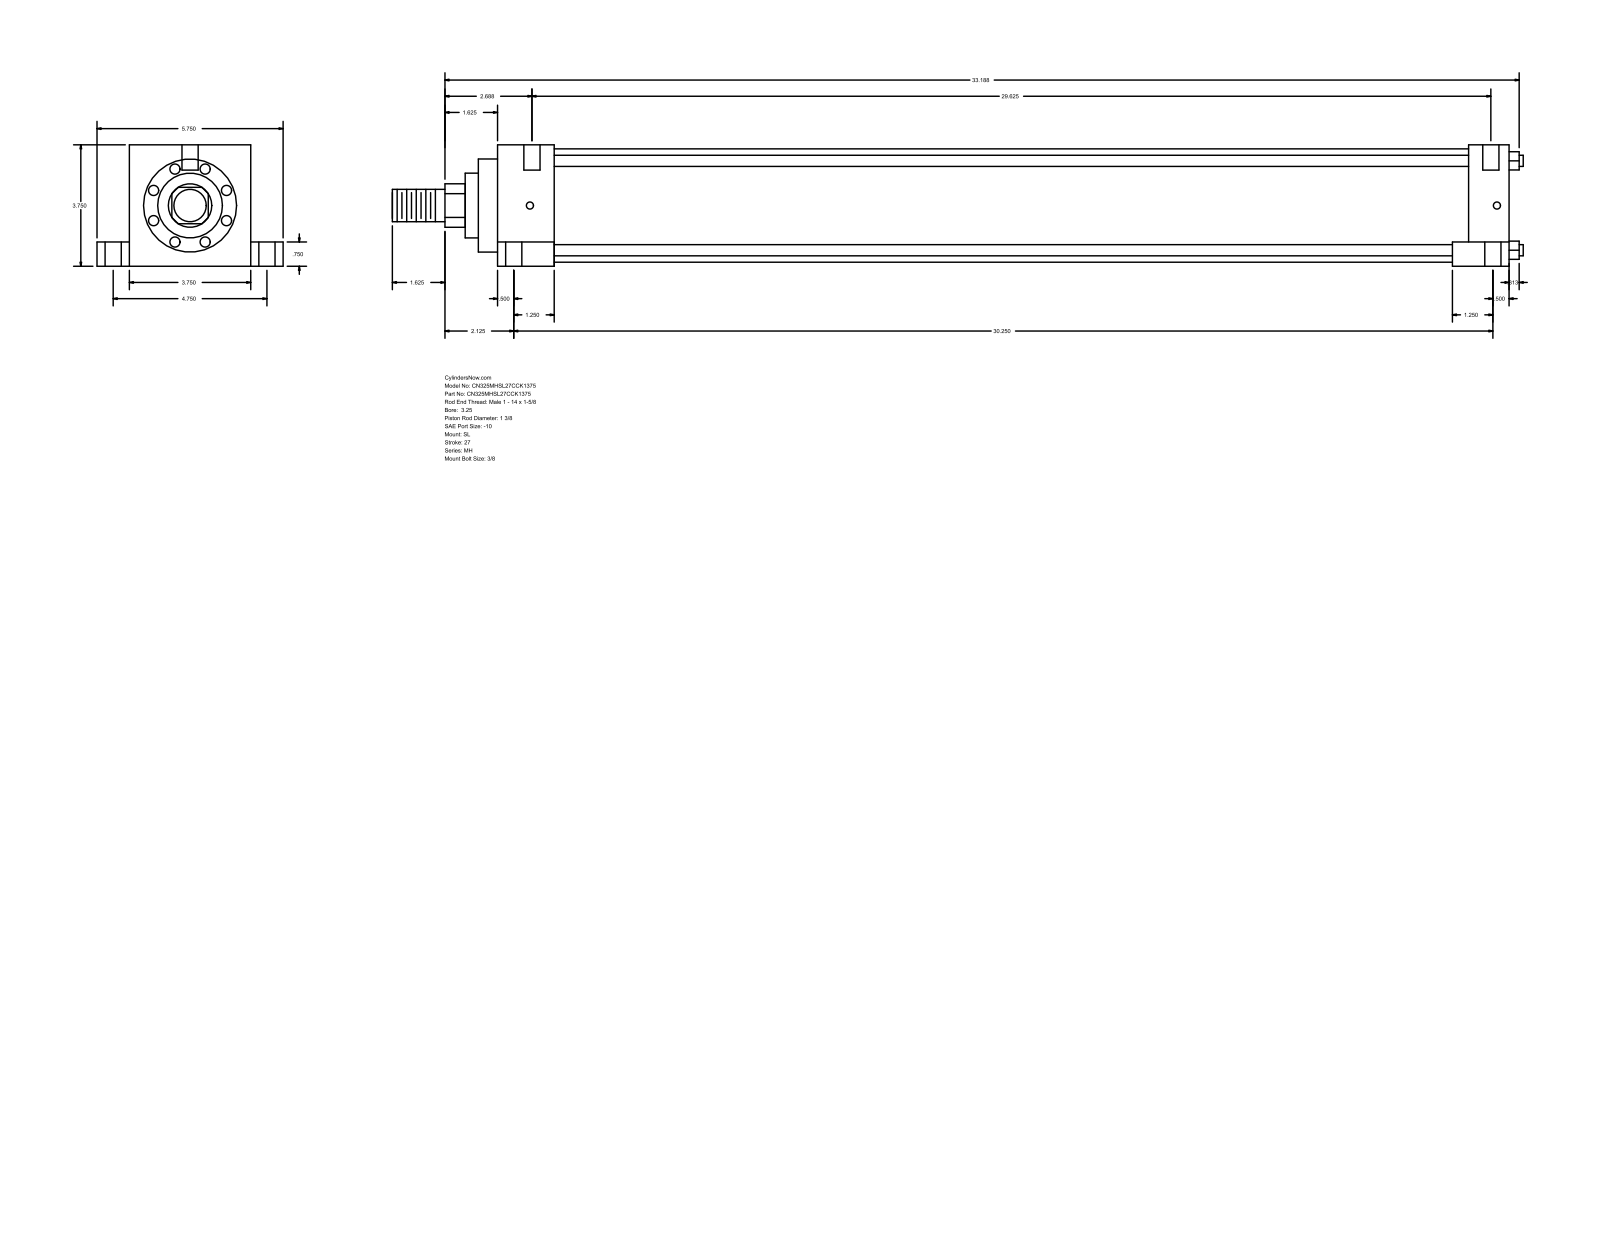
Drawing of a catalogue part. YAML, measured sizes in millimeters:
part_name: "MH_SL__0325_1.375"
step_written_by: "GSSL Pune (CONFIG_CONTROL_DESIGN)"
units: millimeters
bodies: {solids: 0, faces: 110, planar: 77, cylindrical: 33, other: 0}
overall_size: [887.41, 146.05, 95.25]
round_holes:
  - {diameter: 12.7, count: 6}
  - {diameter: 5.56, count: 4}
  - {diameter: 19.05, count: 4}
round_bosses_or_shafts:
  - {diameter: 8.76, count: 4}
  - {diameter: 88.9, count: 1}
  - {diameter: 73.03, count: 1}
  - {diameter: 50.8, count: 1}
  - {diameter: 34.92, count: 1}
  - {diameter: 25.4, count: 1}
partial_cylinders:
  - {radius: 17.06, count: 1}
face_to_face_distances: [95.24, 793.75, 44.45, 749.3, 25.41, 120.65, 19.05, 76.19, 762, 717.55]
hole_center_spacings: [60.35, 60.41, 61.65, 62, 120.66, 756.48, 758.06, 758.83]
